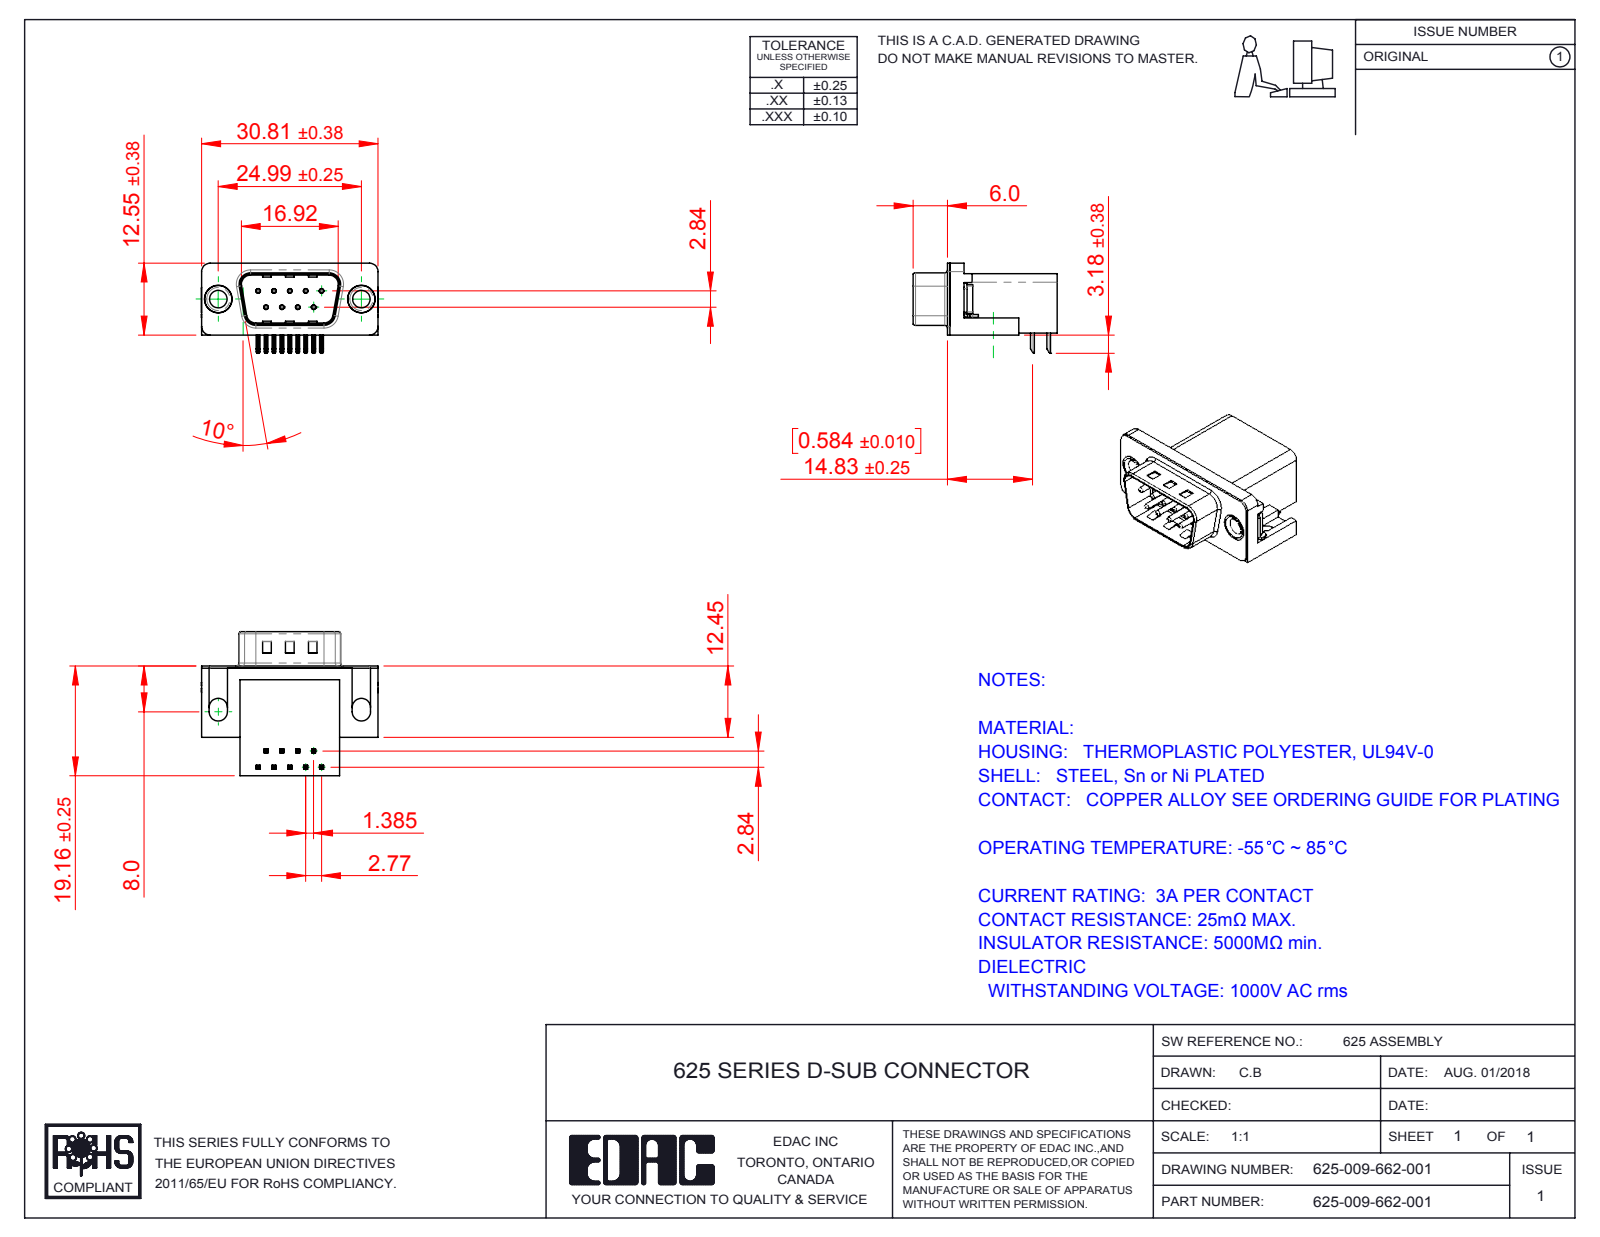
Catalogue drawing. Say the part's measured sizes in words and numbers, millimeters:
The part is named "625 Housing_9 Socket; 625 Non Board Mount; 625 Shell_9 Socket; 625 Thru Hole Rivet (+3 more)". Its 3-D file was written by "SolidWorks 2016 (CONFIG_CONTROL_DESIGN)". It is 15 solids with 951 faces: 575 planar, 295 cylindrical and 81 other. Overall it measures 30.89 by 25.16 by 15.73 millimeters. Its volume is 4 436 cubic millimeters and its surface area 4 794 square millimeters. Round holes: 9 of diameter 0.35, 9 of diameter 0.8, 2 of diameter 3.05, 2 of diameter 4, 2 of diameter 4.8, 2 of diameter 5. Round bosses or shafts: 9 of diameter 0.75, 2 of diameter 4.9, 2 of diameter 4.75, 2 of diameter 3.85. Partial cylindrical surfaces (rounded edges, fillets, slot ends): 44 of radius 0.25, 18 of radius 0.12, 16 of radius 1, 9 of radius 0.5, 8 of radius 1.5, 8 of radius 1.6, 4 of radius 0.9, 4 of radius 2. The main face-to-face distances are 0.4, 10.34, 18.76, 19.16, 2.9, 16.26, 2.5, 0.35, 10.69, 6.7. The hole center spacings are 3.16, 2.77, 5.54, 5.03, 5.04, 8.31, 7.48, 7.49.
